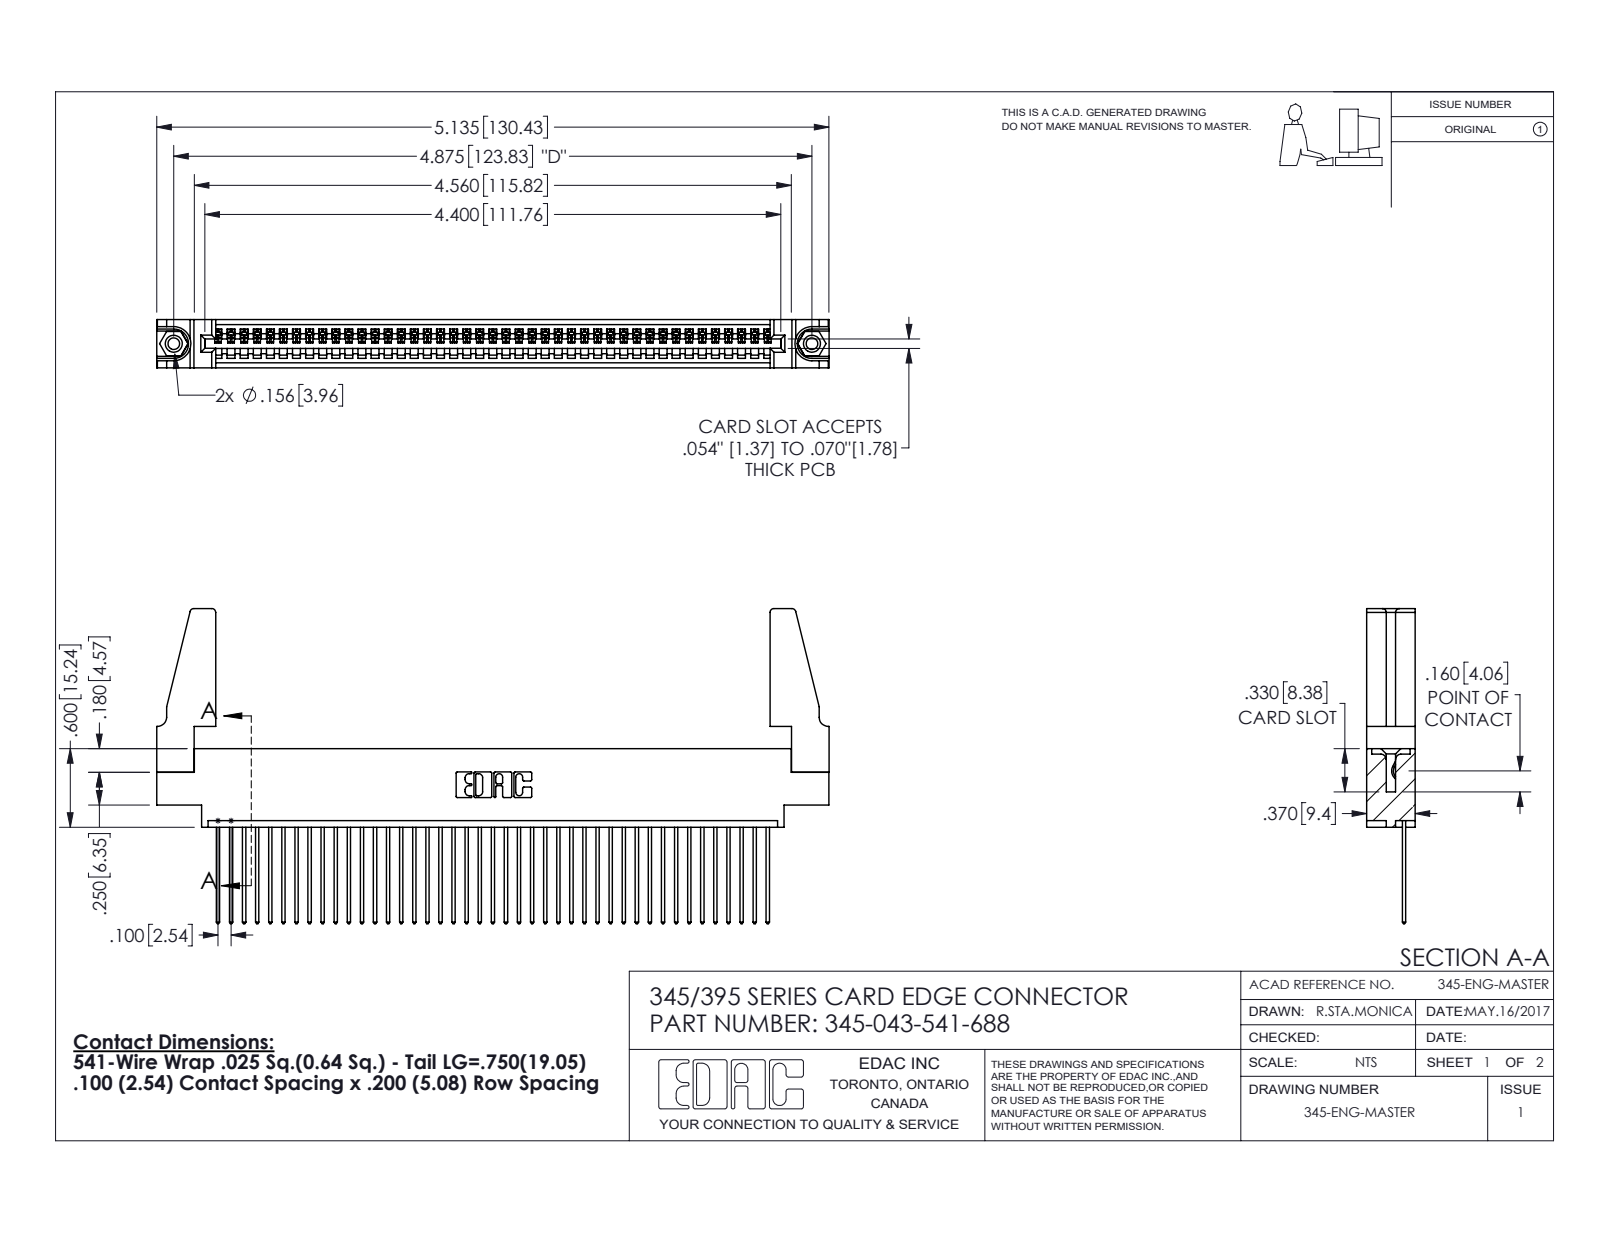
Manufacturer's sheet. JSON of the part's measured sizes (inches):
{"part_name": "345-220-078_345-220-088; 345 Part_0.170 Offset - 0.156 Dia-TH; 345-292-001_345-293-141; 345-250-001_345-250-001-102 (+1 more)", "step_written_by": "SolidWorks 2016 (CONFIG_CONTROL_DESIGN)", "units": "inches", "bodies": {"solids": 48, "faces": 2748, "planar": 1876, "cylindrical": 856, "other": 16}, "overall_size": [5.136, 2.407, 0.37], "volume_in3": 0.957, "surface_area_in2": 31.96, "round_holes": [[0.089, 2], [0.125, 2], [0.156, 2], [0.064, 1]], "round_bosses_or_shafts": [[0.155, 2]], "partial_cylinders_radius": [[0.006, 86], [0.01, 86], [0.01, 22], [0.03, 8], [0.007, 6], [0.031, 6], [0.026, 3], [0.031, 2]], "face_to_face_distances": [0.072, 0.298, 0.37, 0.098, 0.272, 0.025, 0.2, 0.225, 0.175, 0.149], "hole_center_spacings": [0.27, 4.639, 4.875]}
